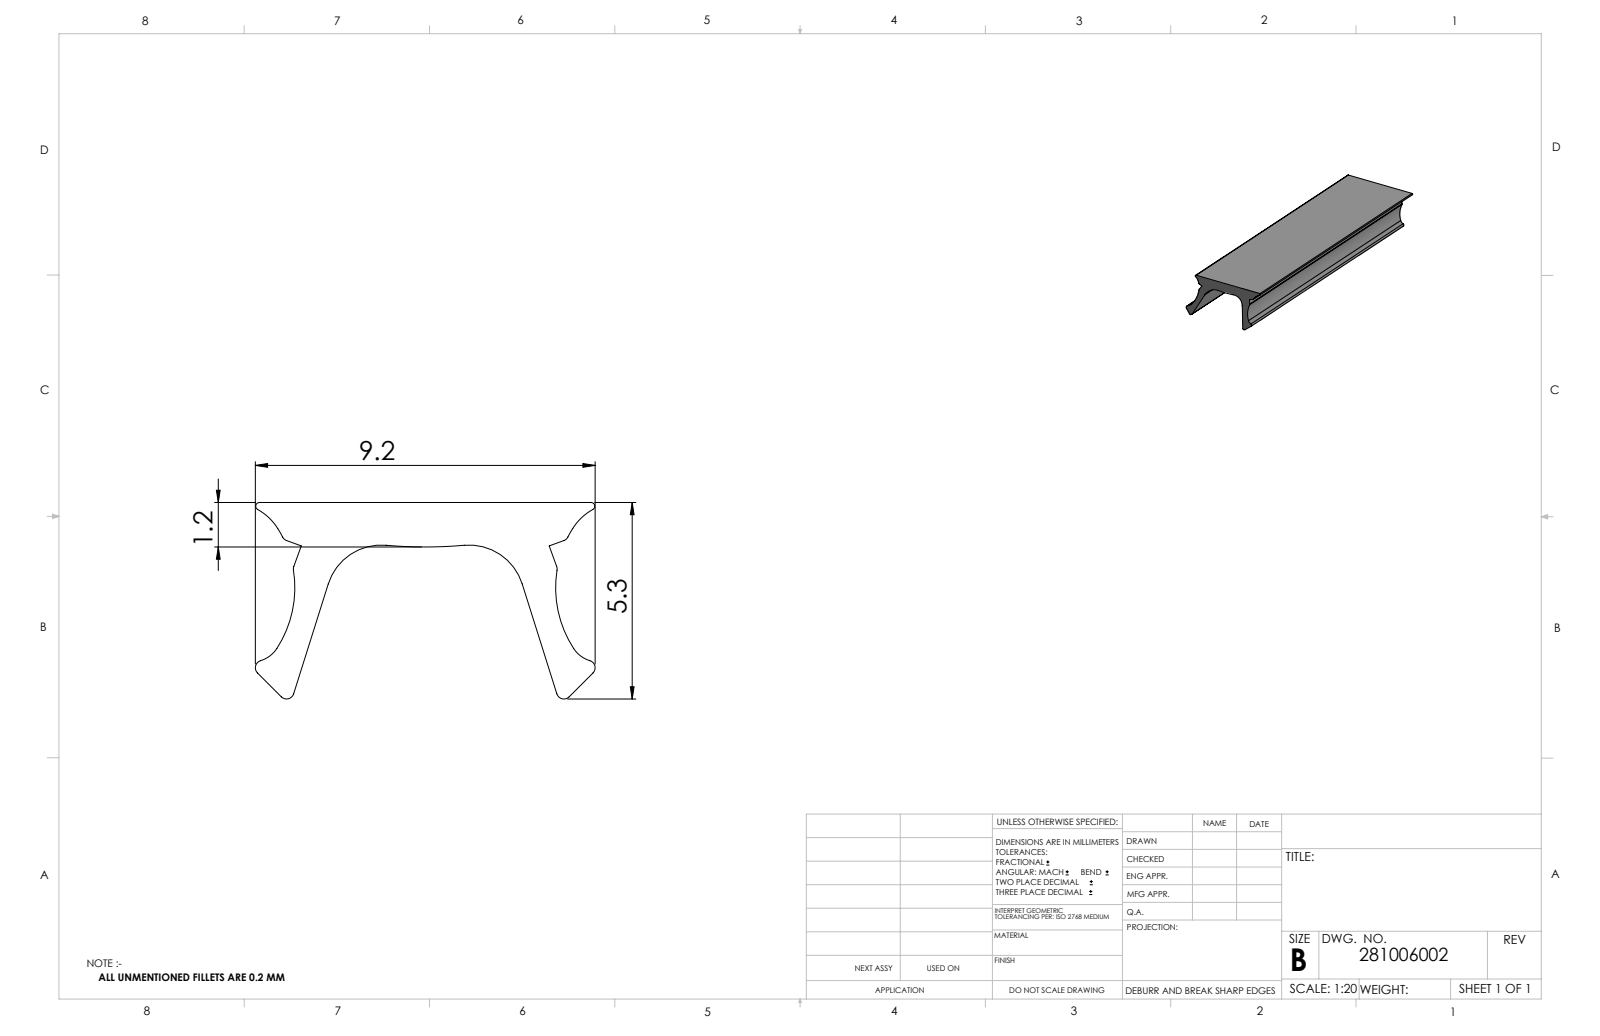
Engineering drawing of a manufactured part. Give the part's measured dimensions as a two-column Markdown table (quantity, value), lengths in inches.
| quantity | value |
| --- | --- |
| part name | 281006002_c_1 |
| STEP written by | SolidWorks 2014 (CONFIG_CONTROL_DESIGN) |
| units | inches |
| bodies | 1 solid, 36 faces (11 planar, 25 cylindrical, 0 other) |
| overall size | 74.803 × 0.361 × 0.209 |
| volume | 1.997 in³ |
| surface area | 104.4 in² |
| partial cylindrical surfaces (radius × count) | 0.008 × 8, 0.059 × 4, 0.004 × 2, 0.031 × 2, 0.118 × 2, 0.472 × 1 |
| main face-to-face distances | 74.803 |
